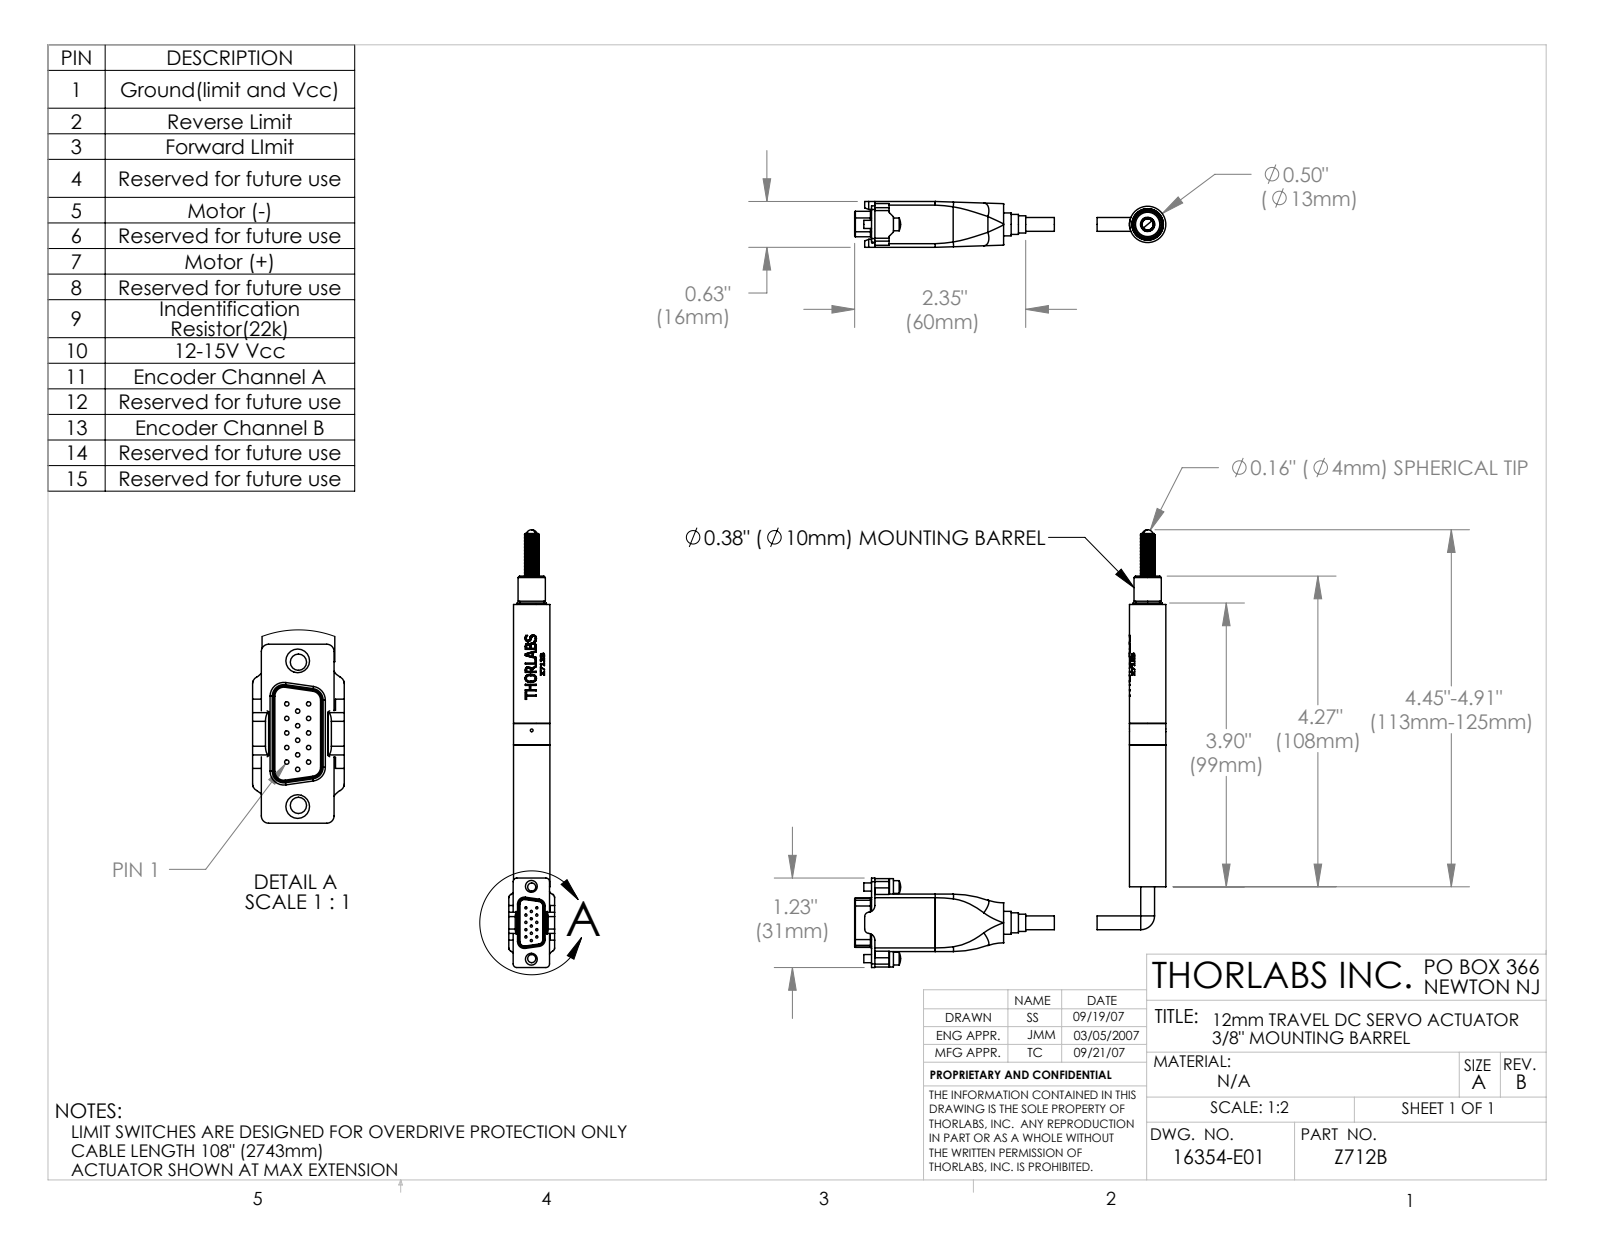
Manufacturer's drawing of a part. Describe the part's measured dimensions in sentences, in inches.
The part is named "Z6 Leadscrew_Z612 Leadscrew; 3501-12V2561; dc-micromotor; 16354-E0W (+8 more)". Its 3-D file was written by "SolidWorks 2007 (CONFIG_CONTROL_DESIGN)". It is 12 solids with 1029 faces: 384 planar, 476 cylindrical and 169 other. Overall it measures 5.777 by 4.279 by 0.63 inches. Its volume is 1.473 cubic inches and its surface area 36.28 square inches. Round holes: 15 of diameter 0.02, 2 of diameter 0.04, 2 of diameter 0.163, 1 of diameter 0.038, 1 of diameter 0.05, 1 of diameter 0.063, 1 of diameter 0.08, 1 of diameter 0.094, 1 of diameter 0.156, 1 of diameter 0.18, 1 of diameter 0.188, 1 of diameter 0.19. Round bosses or shafts: 15 of diameter 0.03, 2 of diameter 0.175, 2 of diameter 0.112, 1 of diameter 0.55, 1 of diameter 0.5, 1 of diameter 0.479, 1 of diameter 0.44, 1 of diameter 0.403. Partial cylindrical surfaces (rounded edges, fillets, slot ends): 8 of radius 0.01, 8 of radius 0.015, 8 of radius 0.04, 6 of radius 0.02, 6 of radius 0.05, 6 of radius 0.06, 6 of radius 0.063, 4 of radius 0.005. The main face-to-face distances are 0.63, 0.79, 0.085, 0.175, 0.545, 0.046, 0.221, 0.018, 0.14, 0.1. The hole center spacings are 0.09, 0.168, 0.1, 0.261, 0.2, 0.18, 0.25, 0.3.
